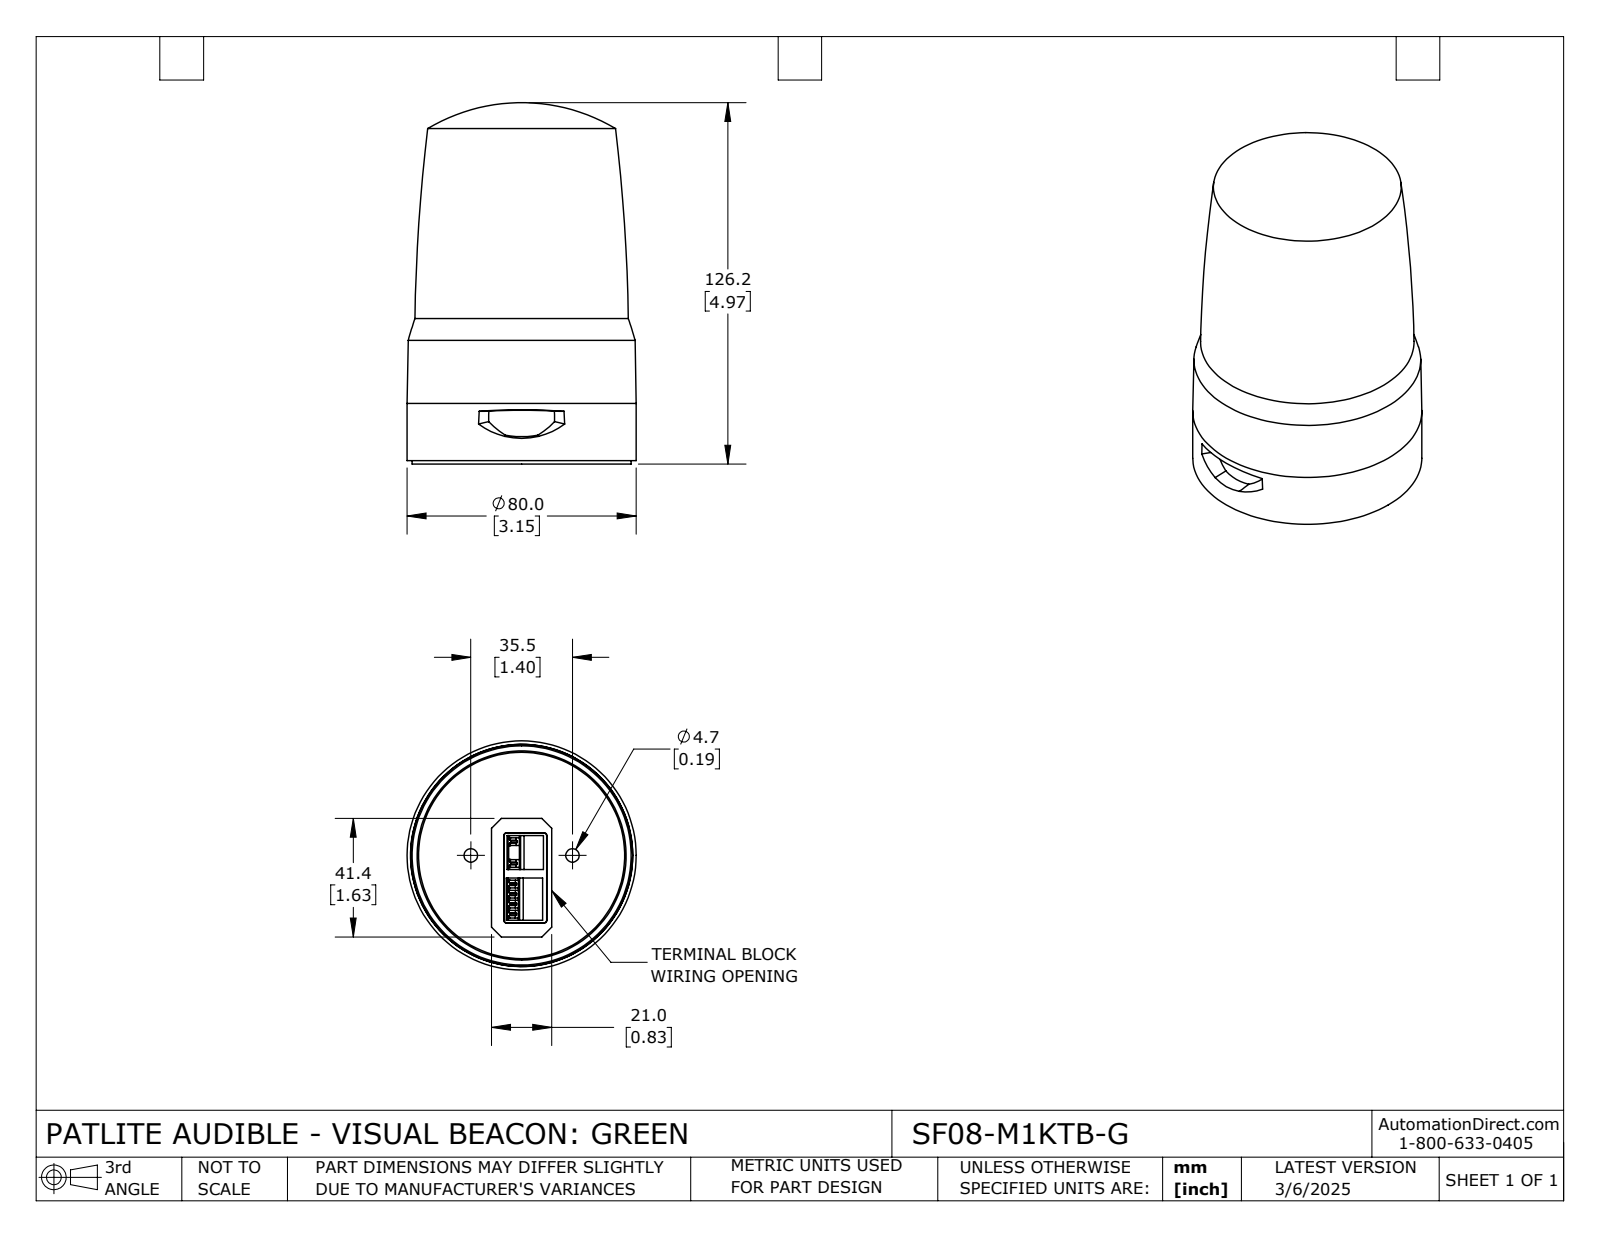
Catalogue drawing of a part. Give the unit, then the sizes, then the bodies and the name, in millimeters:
Units: millimetres
Overall size (bounding box): 126.2 × 80 × 80
Round holes (diameter × count): ⌀4.7 ×2, ⌀12.2 ×2, ⌀73 ×1
Round bosses / shafts (diameter × count): ⌀80 ×1, ⌀76.5 ×1, ⌀74.6 ×1, ⌀72 ×1
Partial cylindrical surfaces — rounded edges, fillets, slot ends (radius × count): R1 ×4, R0.3 ×2, R34.6 ×1, R35 ×1
Main face-to-face distances: 15.7, 6.3, 9.4, 3, 5.1, 14.5, 3.15, 6.15, 1.3, 12.45
Hole centre spacings: 17.75, 35.5
Volume: 488 153 mm³ · Surface area: 54 584 mm²
Bodies: 2 solids, 262 faces (168 planar, 32 cylindrical, 62 other)
Part name (STEP PRODUCT): SF08-M1KTB-G
STEP written by: SolidWorks 2024 (CONFIG_CONTROL_DESIGN)
